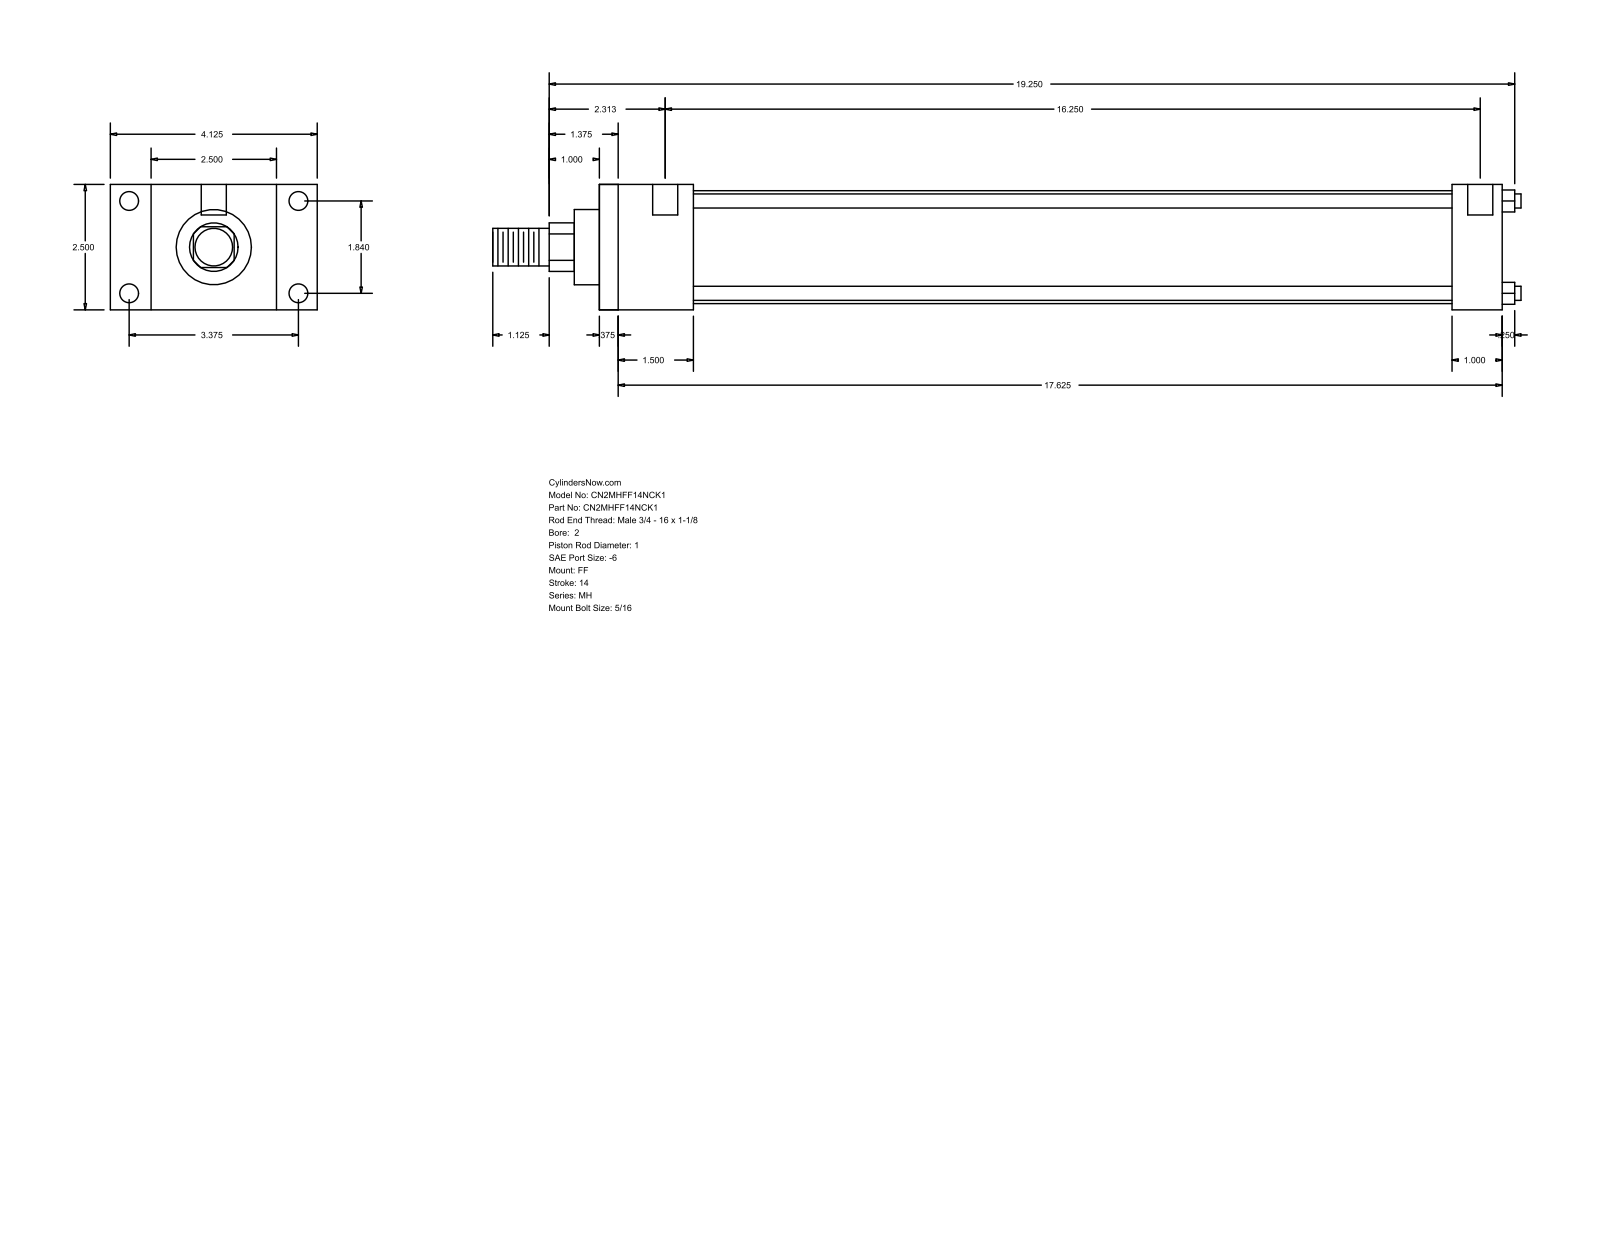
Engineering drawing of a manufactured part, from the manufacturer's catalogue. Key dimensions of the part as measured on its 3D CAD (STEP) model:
Part name (STEP PRODUCT): MH_FF__0200_1
STEP written by: GSSL Pune (CONFIG_CONTROL_DESIGN)
Units: millimetres
Bodies: 0 solids, 92 faces (64 planar, 28 cylindrical, 0 other)
Overall size (bounding box): 520.7 × 104.78 × 63.5
Round holes (diameter × count): ⌀5.56 ×4, ⌀9.53 ×4, ⌀12.7 ×2
Round bosses / shafts (diameter × count): ⌀7.14 ×4, ⌀57.15 ×1, ⌀38.1 ×1, ⌀25.4 ×1, ⌀19.05 ×1
Partial cylindrical surfaces — rounded edges, fillets, slot ends (radius × count): R12.29 ×1
Main face-to-face distances: 63.5, 457.2, 9.52, 447.68, 20.64, 25.4, 47.63, 431.8, 38.11, 422.28
Hole centre spacings: 46.74, 85.72, 97.63, 420.68, 3.17, 4.76, 412.75, 415.92
